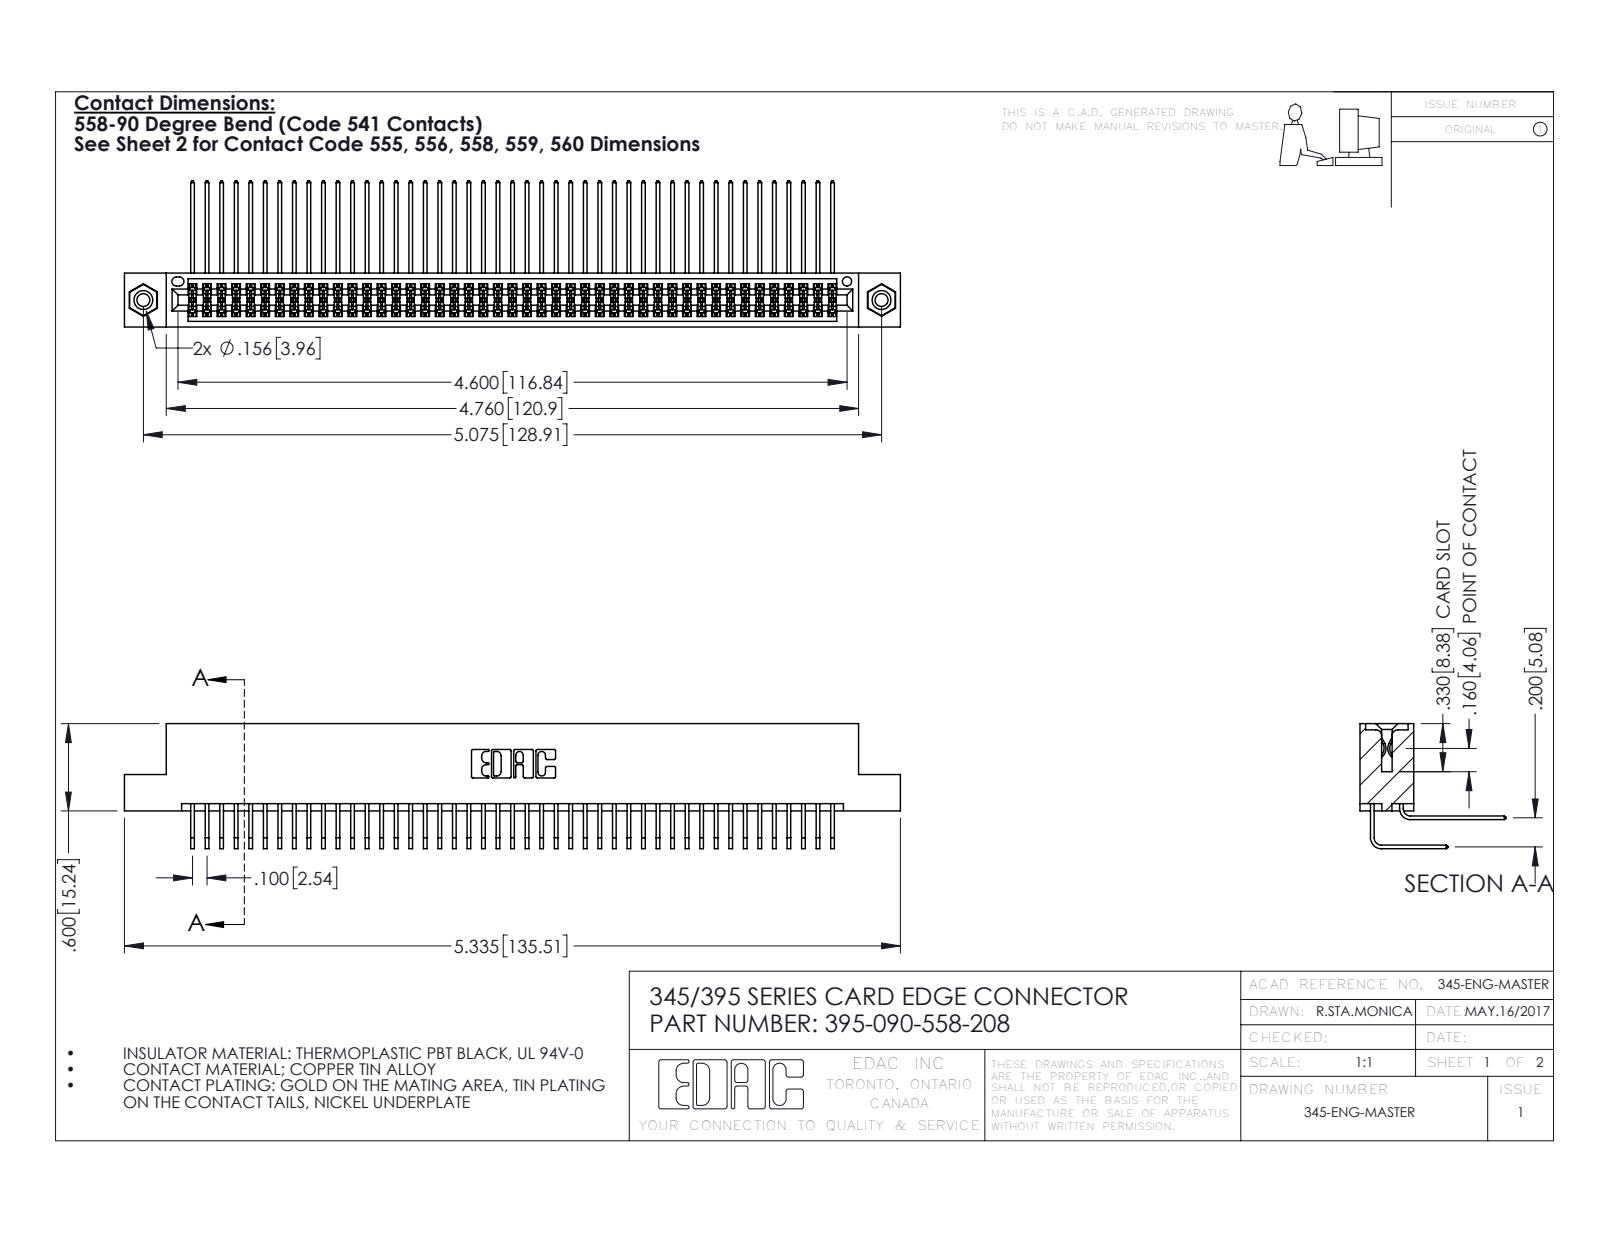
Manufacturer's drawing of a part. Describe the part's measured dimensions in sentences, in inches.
The part is named "345-250-001_345-250-003-102; 345-292-001_558 559 Tail - 1; 345-292-001_558 Tail - 2; 345 Part_Flush Mounting Lugs - 0.156 Dia-TI (+1 more)". Its 3-D file was written by "SolidWorks 2016 (CONFIG_CONTROL_DESIGN)". It is 93 solids with 4866 faces: 3262 planar, 1588 cylindrical and 16 other. Overall it measures 5.335 by 1.005 by 0.859 inches. Its volume is 0.836 cubic inches and its surface area 35.29 square inches. Round holes: 2 of diameter 0.089, 2 of diameter 0.125, 2 of diameter 0.156, 1 of diameter 0.064. Round bosses or shafts: 2 of diameter 0.155. Partial cylindrical surfaces (rounded edges, fillets, slot ends): 136 of radius 0.006, 22 of radius 0.01, 6 of radius 0.007, 6 of radius 0.031, 3 of radius 0.026, 2 of radius 0.014, 2 of radius 0.019, 2 of radius 0.022. The main face-to-face distances are 0.072, 0.298, 0.2, 0.37, 0.098, 0.272, 0.025, 0.225, 0.025, 0.175. The hole center spacings are 0.27, 4.839, 5.075.
